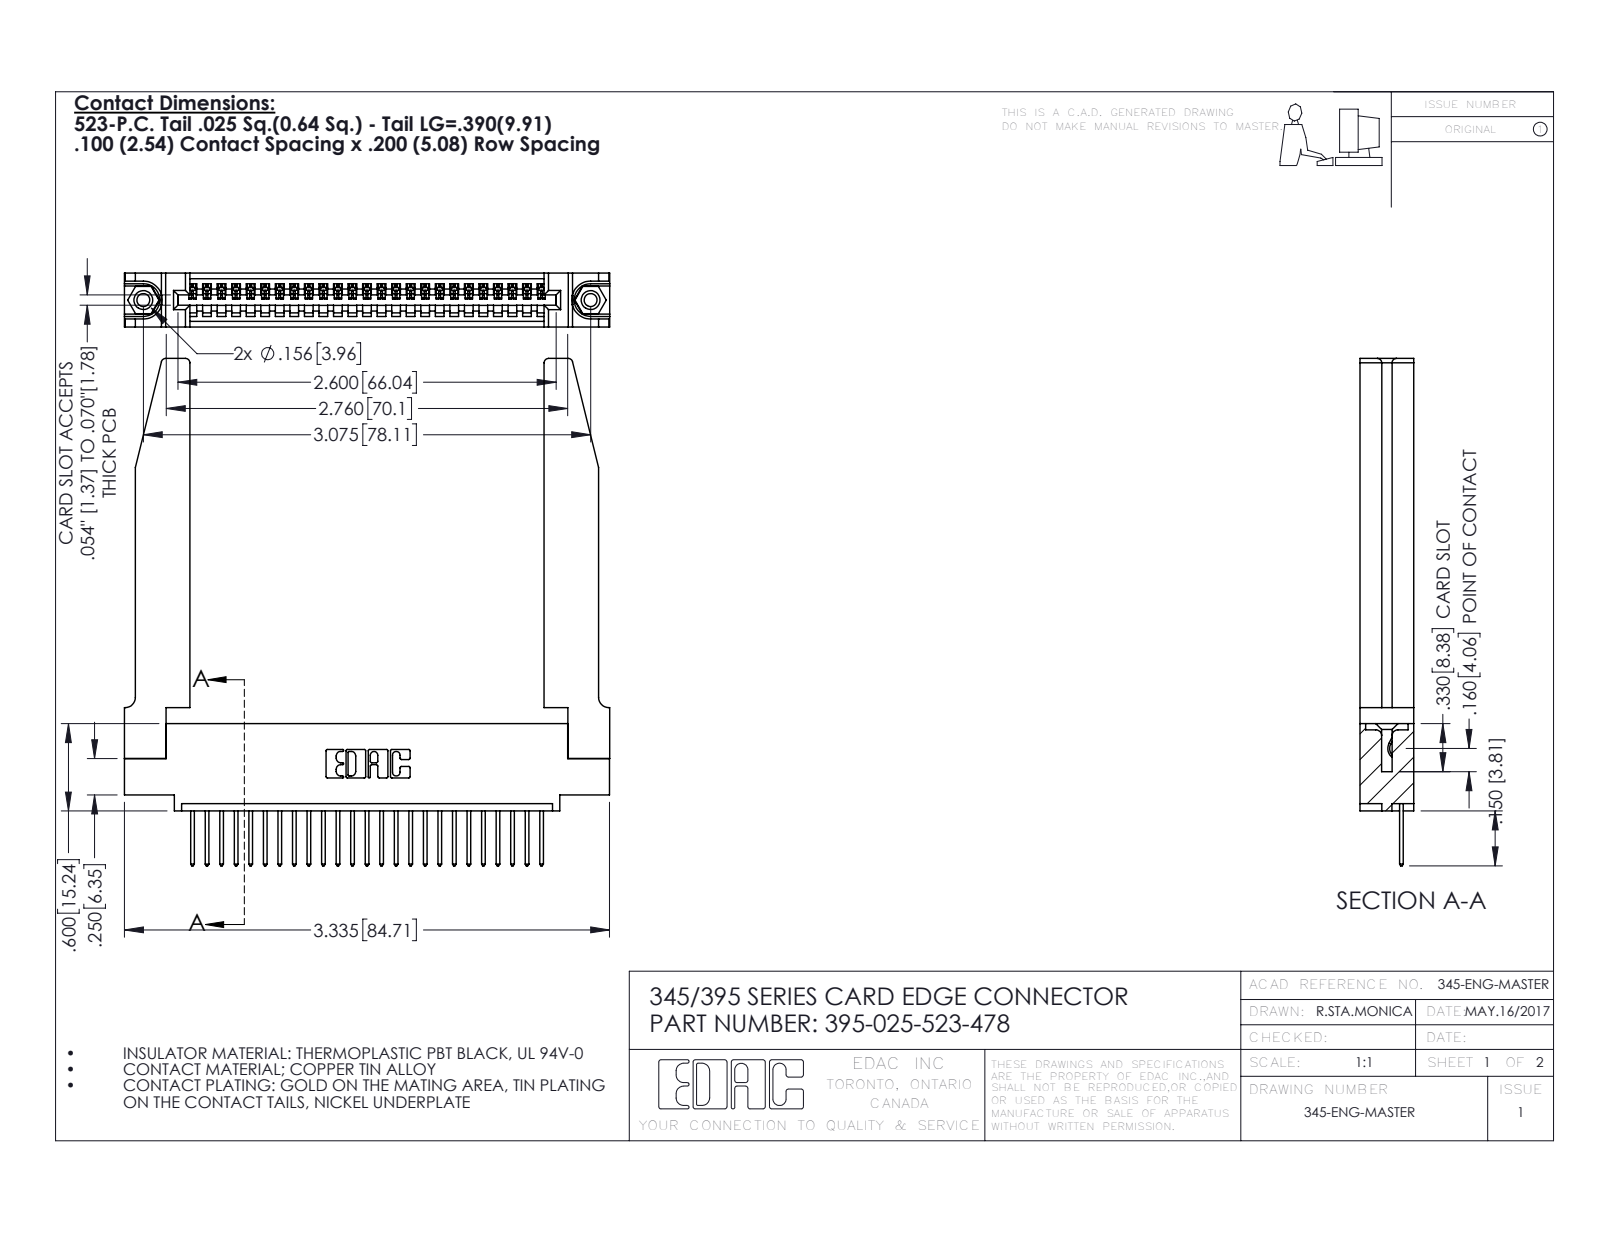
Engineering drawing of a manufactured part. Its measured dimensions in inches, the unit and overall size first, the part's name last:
Units: inches
Overall size (bounding box): 3.487 × 3.336 × 0.37
Round holes (diameter × count): ⌀0.089 ×2, ⌀0.125 ×2, ⌀0.156 ×2, ⌀0.064 ×1
Round bosses / shafts (diameter × count): ⌀0.155 ×2
Partial cylindrical surfaces — rounded edges, fillets, slot ends (radius × count): R0.006 ×50, R0.01 ×50, R0.01 ×22, R0.03 ×8, R0.007 ×6, R0.031 ×6, R0.026 ×3, R0.031 ×2
Main face-to-face distances: 0.37, 0.072, 0.298, 0.098, 0.272, 0.025, 0.2, 0.148, 0.15, 0.225
Hole centre spacings: 0.27, 2.84, 3.075
Volume: 0.952 in³ · Surface area: 26.54 in²
Bodies: 30 solids, 1814 faces (1226 planar, 536 cylindrical, 52 other)
Part name (STEP PRODUCT): 345-250-001_345-250-001-102; 345-292-001_345-293-123; 345 Part_0.110 Offset - 0.156 Dia-TH; 395-025-523-478 (+1 more)
STEP written by: SolidWorks 2016 (CONFIG_CONTROL_DESIGN)
